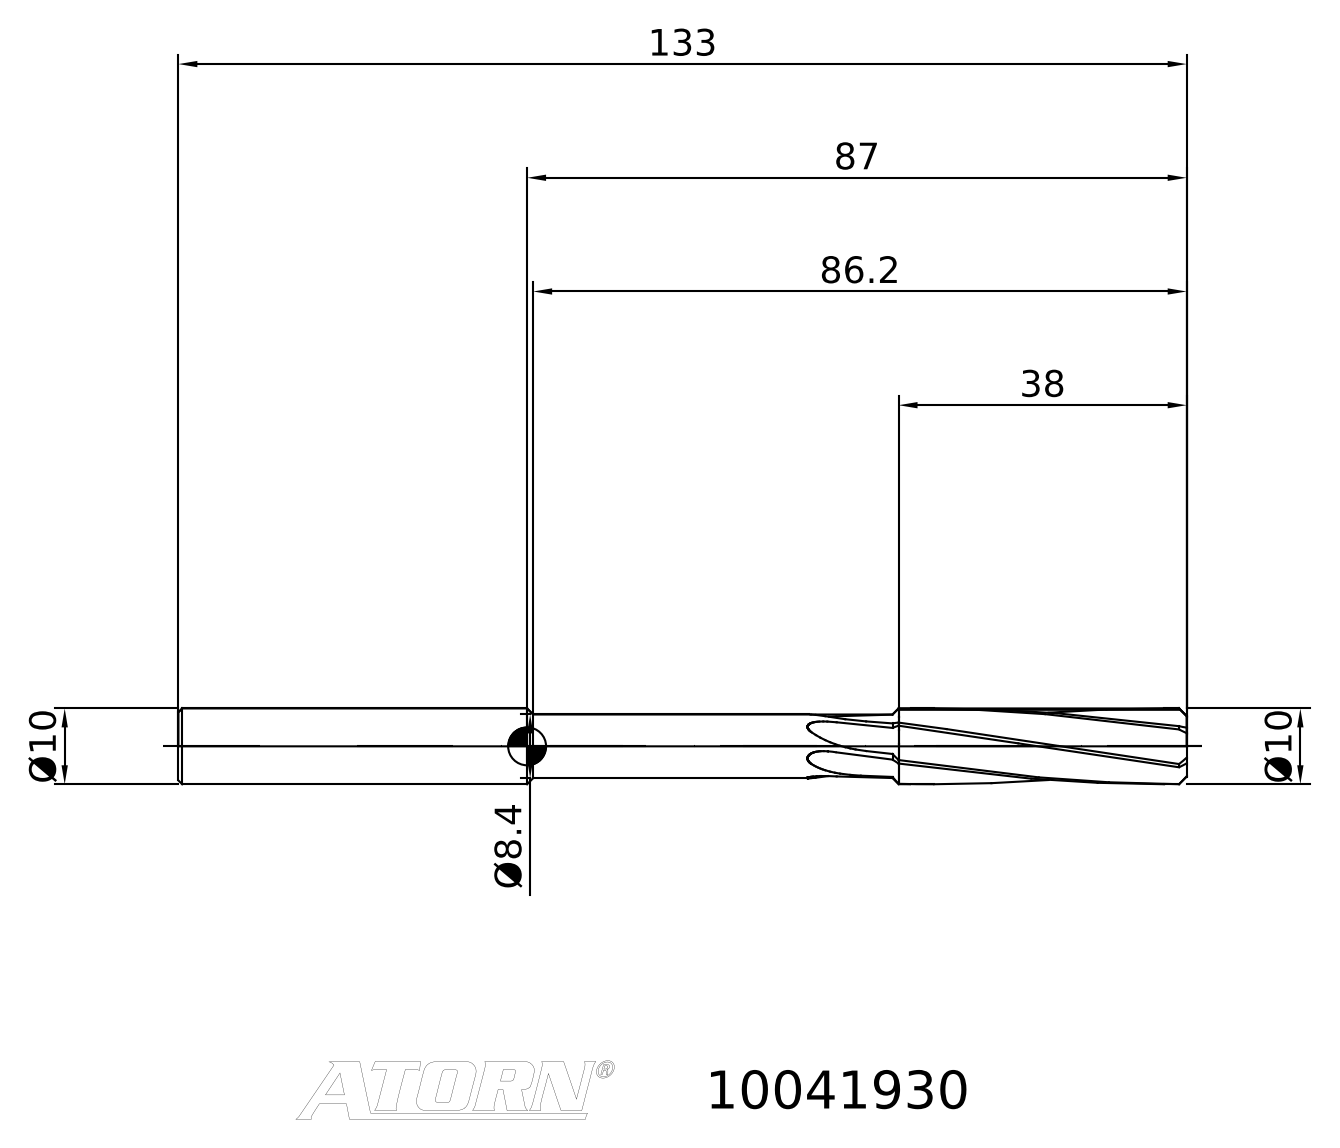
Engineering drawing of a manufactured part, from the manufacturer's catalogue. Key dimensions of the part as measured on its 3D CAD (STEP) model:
STEP written by: TDM (AUTOMOTIVE_DESIGN)
Units: millimetres
Bodies: 2 solids, 65 faces (4 planar, 0 cylindrical, 61 other)
Overall size (bounding box): 133 × 10.82 × 10
Volume: 7 520 mm³ · Surface area: 4 511 mm²
Main face-to-face distances: 95, 38, 133
